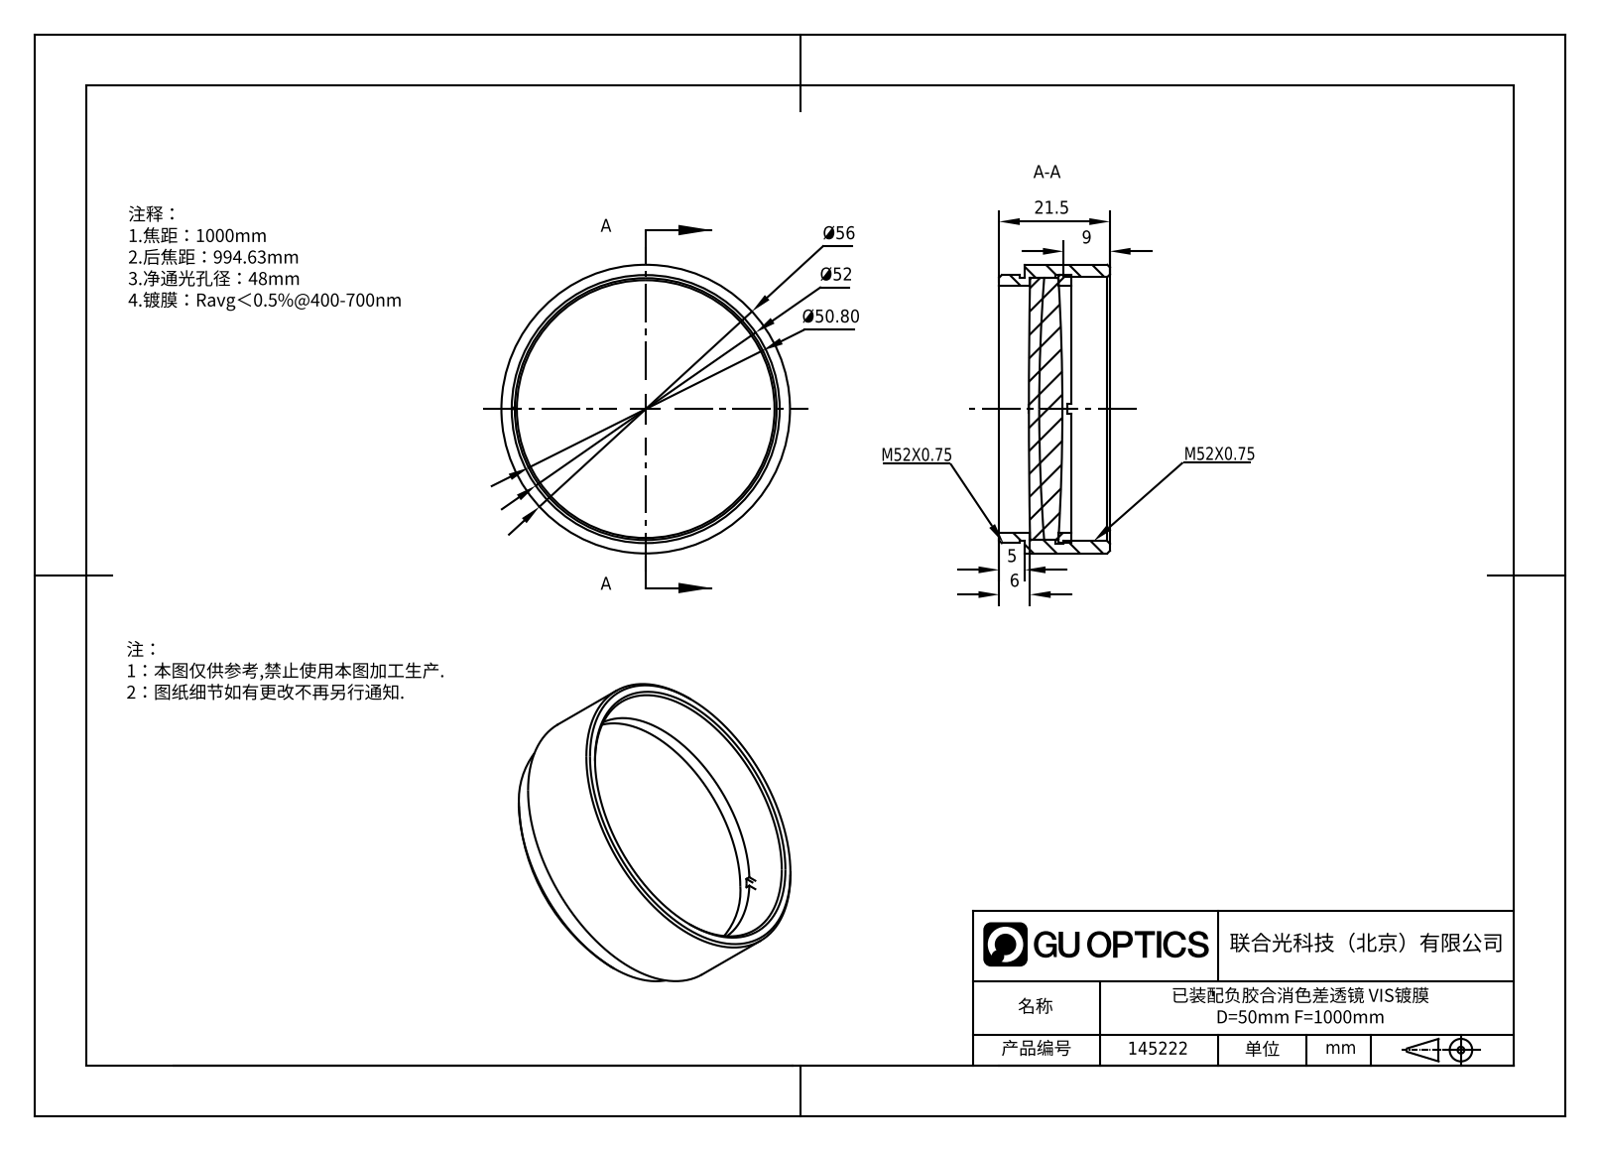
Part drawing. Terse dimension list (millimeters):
name: GL31-050B-1000-VIS_Solidworks; APD-ML50-1000-VIS; M52x0.75安装环-PN35002-LM508-D1; M52x0.75ѹȦ
written by: SolidWorks 2022 (AUTOMOTIVE_DESIGN)
unit: mm
bodies: 4 solids, 58 faces (16 planar, 22 cylindrical, 20 other)
size: 56 × 56 × 21.5
volume: 20 463 mm³; area: 18 875 mm²
holes: 1× ⌀48, 1× ⌀51.25, 1× ⌀52.1
bosses: 1× ⌀56, 1× ⌀52, 1× ⌀51, 1× ⌀50.8
face distances: 7.75, 5, 6, 8.75, 1, 6.25, 2.5, 11.25, 13.75, 21.5
